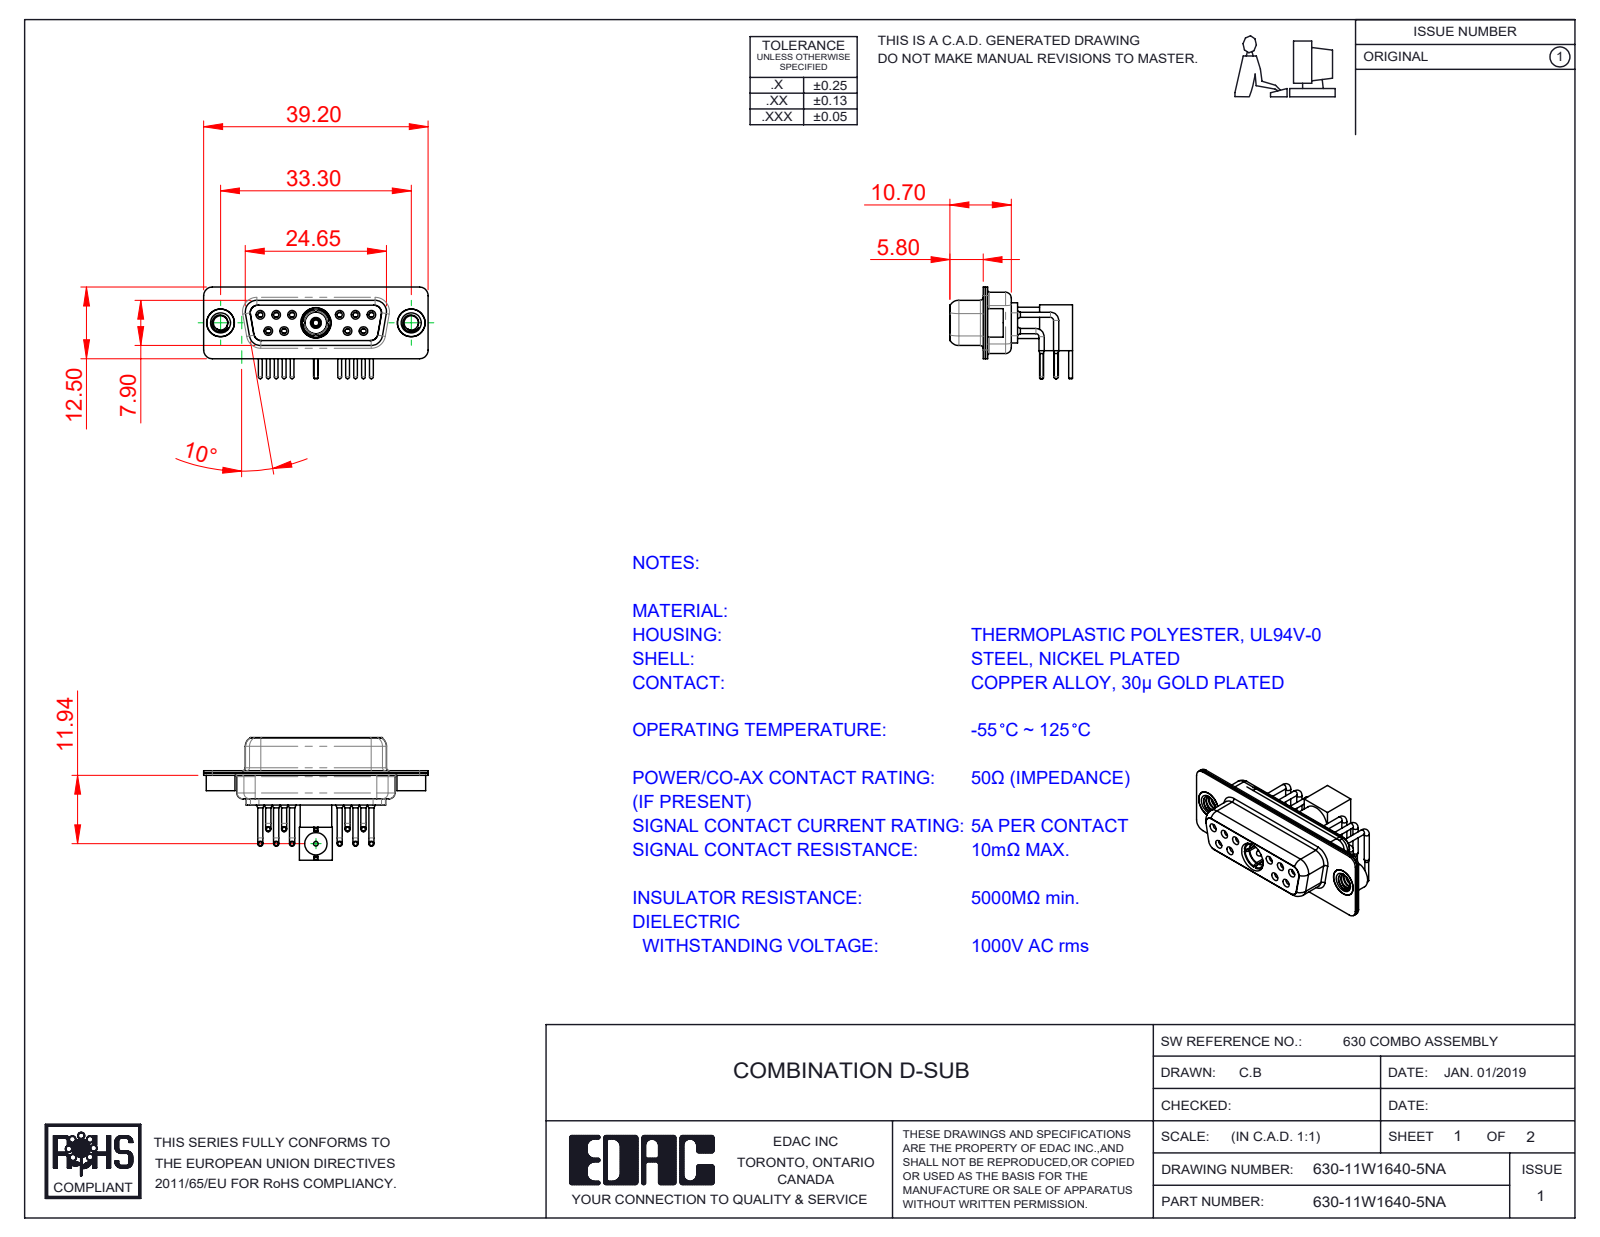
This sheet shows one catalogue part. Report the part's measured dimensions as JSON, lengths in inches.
{"part_name": "630Combo Shell Rear_15 Contacts; Pin_RA; RA Back Shell; Insulator RA Pin (+8 more)", "step_written_by": "SolidWorks 2020 (CONFIG_CONTROL_DESIGN)", "units": "inches", "bodies": {"solids": 21, "faces": 971, "planar": 284, "cylindrical": 430, "other": 257}, "overall_size": [1.543, 0.843, 0.63], "volume_in3": 0.171, "surface_area_in2": 10.69, "round_holes": [[0.043, 11], [0.059, 11], [0.035, 10], [0.079, 10], [0.067, 6], [0.063, 4], [0.191, 3], [0.098, 2], [0.157, 2], [0.159, 2], [0.031, 1], [0.111, 1]], "round_bosses_or_shafts": [[0.035, 10], [0.026, 10], [0.063, 6], [0.197, 3], [0.195, 2], [0.189, 2], [0.217, 1], [0.205, 1]], "partial_cylinders_radius": [[0.059, 16], [0.053, 12], [0.079, 12], [0.063, 8], [0.01, 4], [0.02, 4], [0.024, 4], [0.026, 4]], "face_to_face_distances": [0.016, 0.055, 0.018, 0.071, 0.333, 0.031, 0.35, 0.244, 0.278, 0.073], "hole_center_spacings": [0.124, 0.109, 0.545, 0.436, 0.654, 0.198, 0.198, 0.218]}
